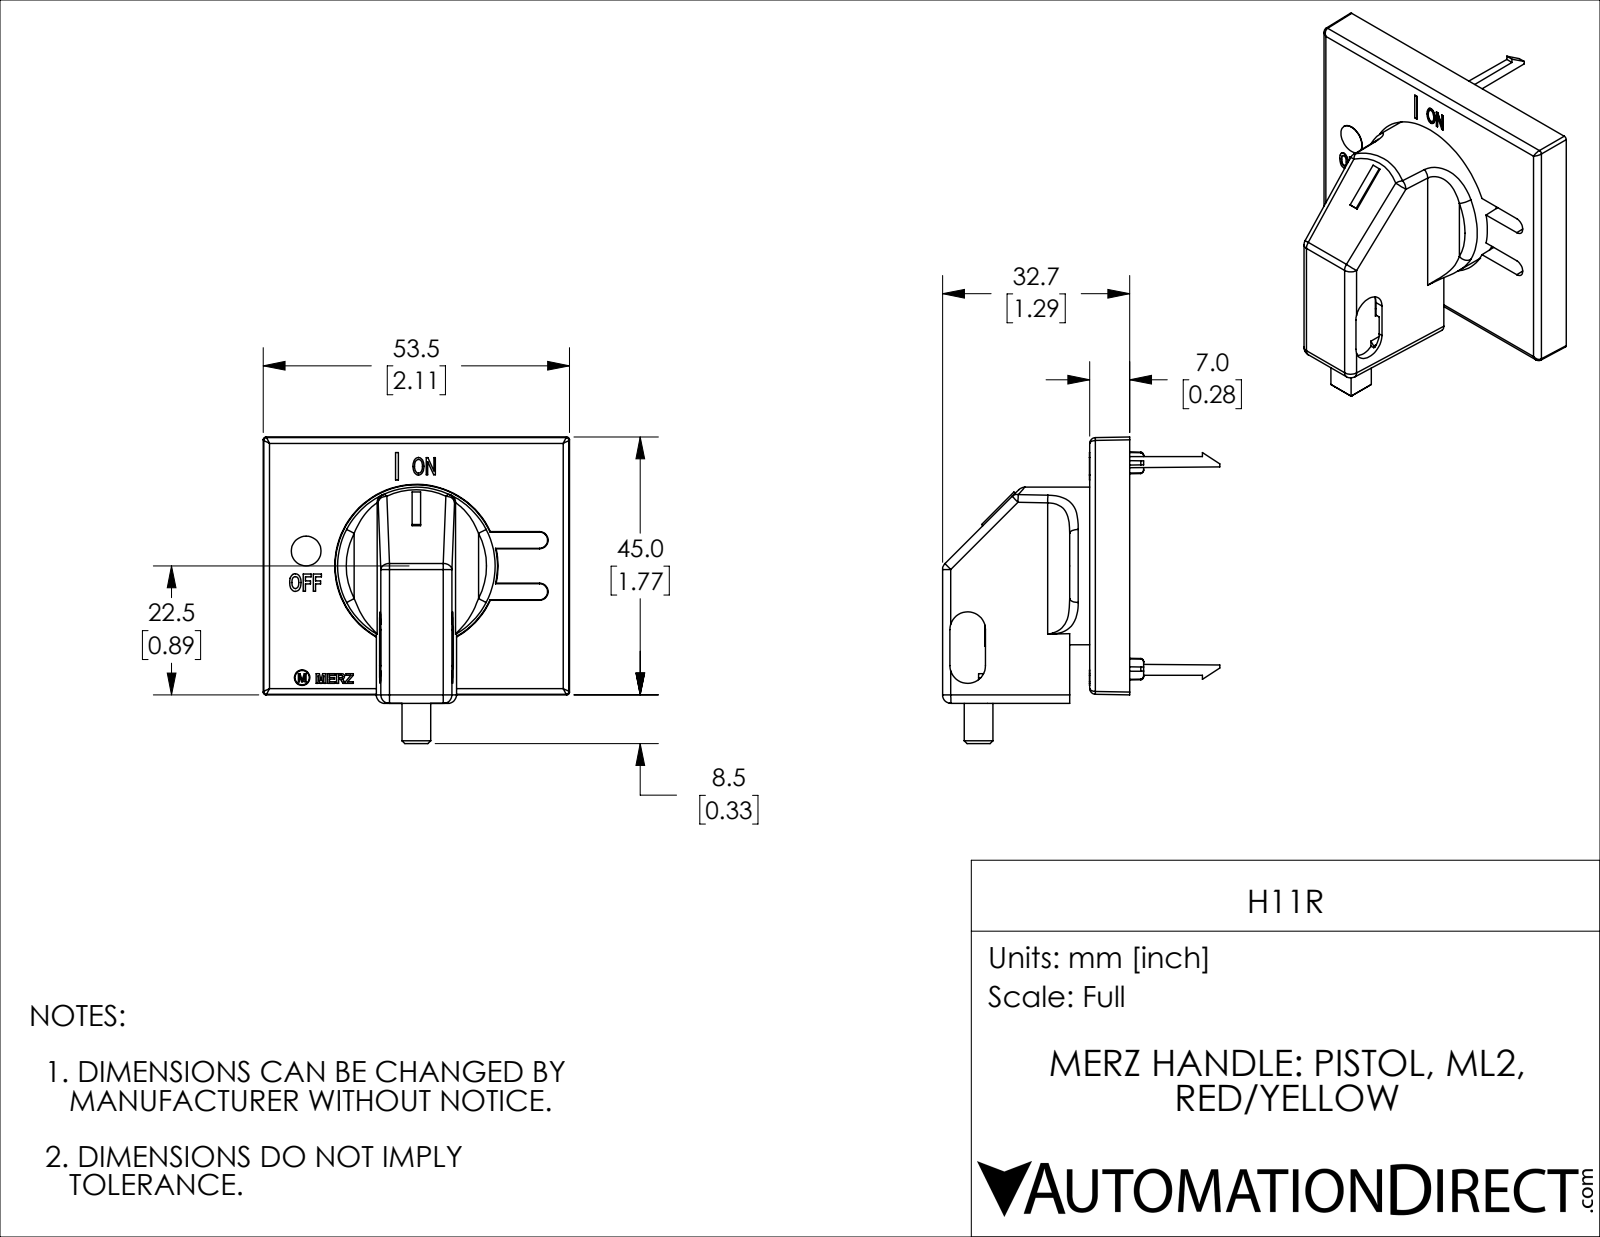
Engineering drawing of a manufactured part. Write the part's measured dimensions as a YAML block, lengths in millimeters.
part_name: "H11R"
step_written_by: "SolidWorks 2019 (AUTOMOTIVE_DESIGN)"
units: millimeters
bodies: {solids: 2, faces: 439, planar: 290, cylindrical: 42, other: 107}
overall_size: [53.5, 53.5, 48.4]
volume: 16700
surface_area: 15570
round_holes:
  - {diameter: 2.5, count: 1}
round_bosses_or_shafts:
  - {diameter: 27.5, count: 1}
  - {diameter: 5.2, count: 1}
  - {diameter: 2.7, count: 1}
partial_cylinders:
  - {radius: 1.5, count: 8}
  - {radius: 0.5, count: 6}
  - {radius: 0.3, count: 5}
  - {radius: 1, count: 4}
  - {radius: 3.1, count: 2}
  - {radius: 4, count: 2}
face_to_face_distances: [1, 2, 4, 5, 3, 6, 7, 8.3, 0.8, 2.4]
